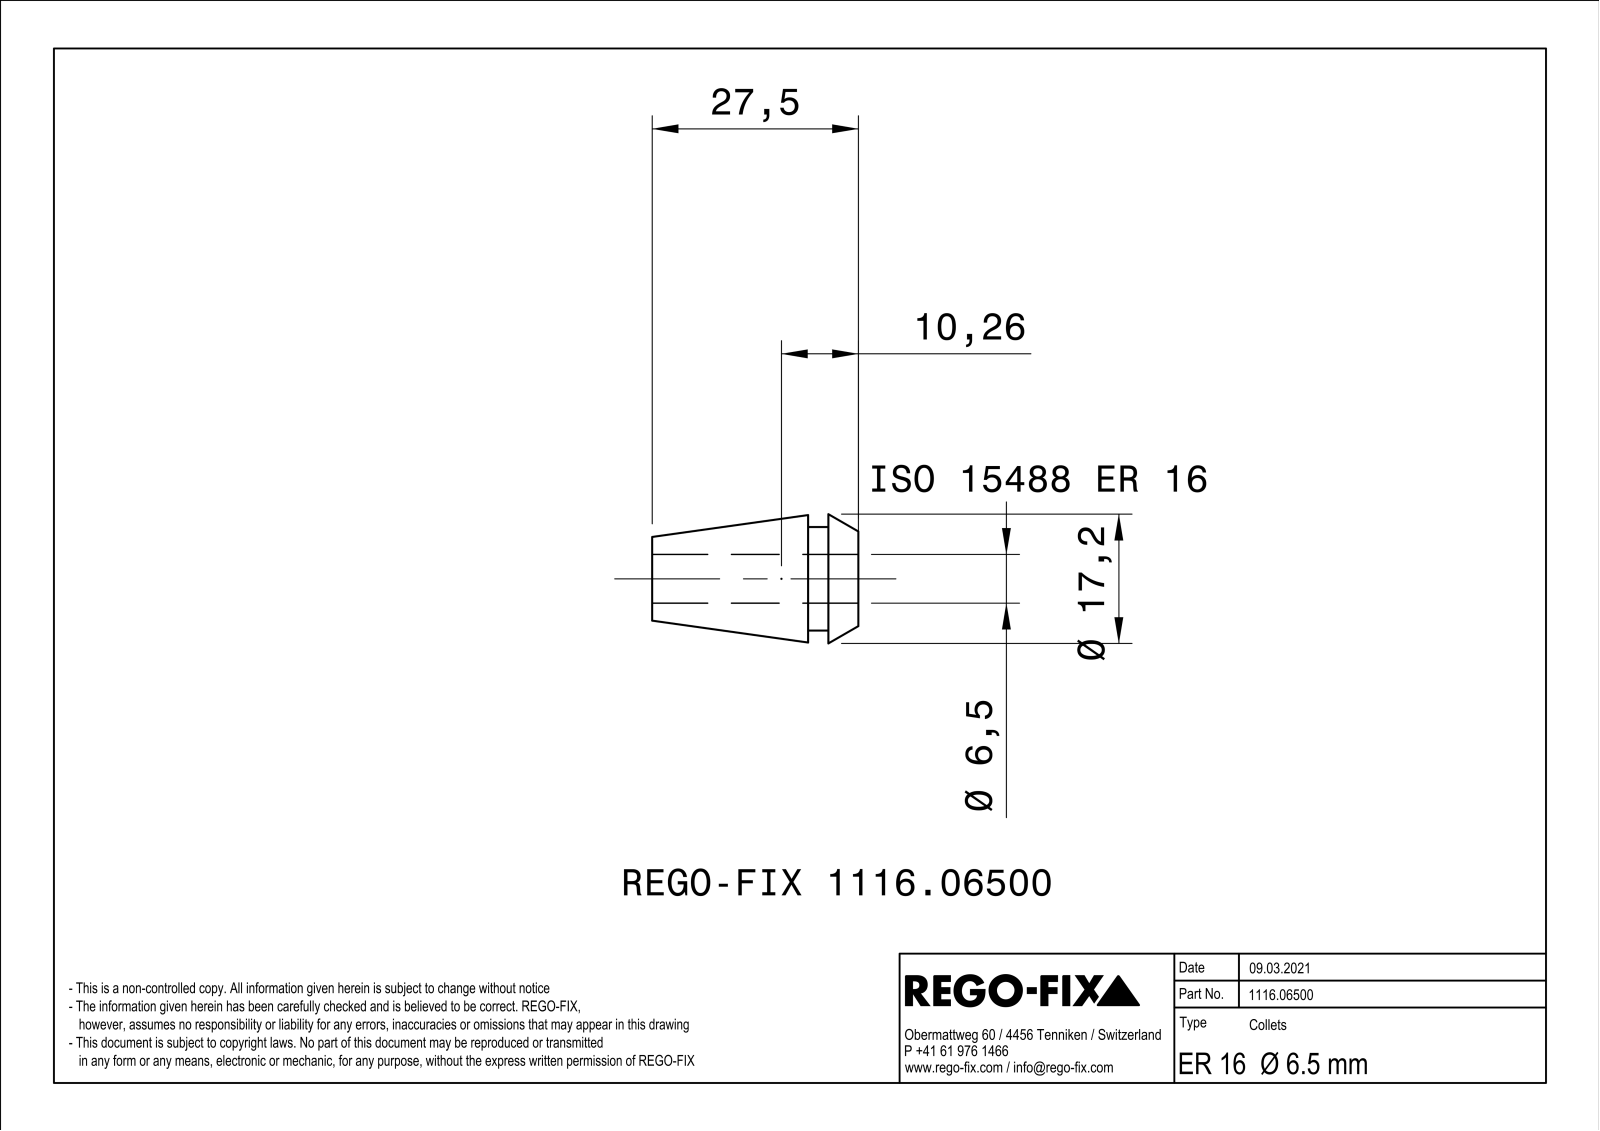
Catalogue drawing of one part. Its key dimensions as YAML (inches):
part_name: "NOCUT"
step_written_by: "SIEMENS PLM Software Solid Edge ST10 (AUTOMOTIVE_DESIGN)"
units: inches
bodies: {solids: 1, faces: 153, planar: 72, cylindrical: 25, other: 56}
overall_size: [1.083, 0.679, 0.679]
volume: 0.158
surface_area: 7.173
round_holes:
  - {diameter: 0.256, count: 1}
round_bosses_or_shafts:
  - {diameter: 0.543, count: 1}
partial_cylinders:
  - {radius: 0.012, count: 8}
face_to_face_distances: [0.024, 0.157, 0.264, 0.106, 1.083, 0.925, 0.819]
